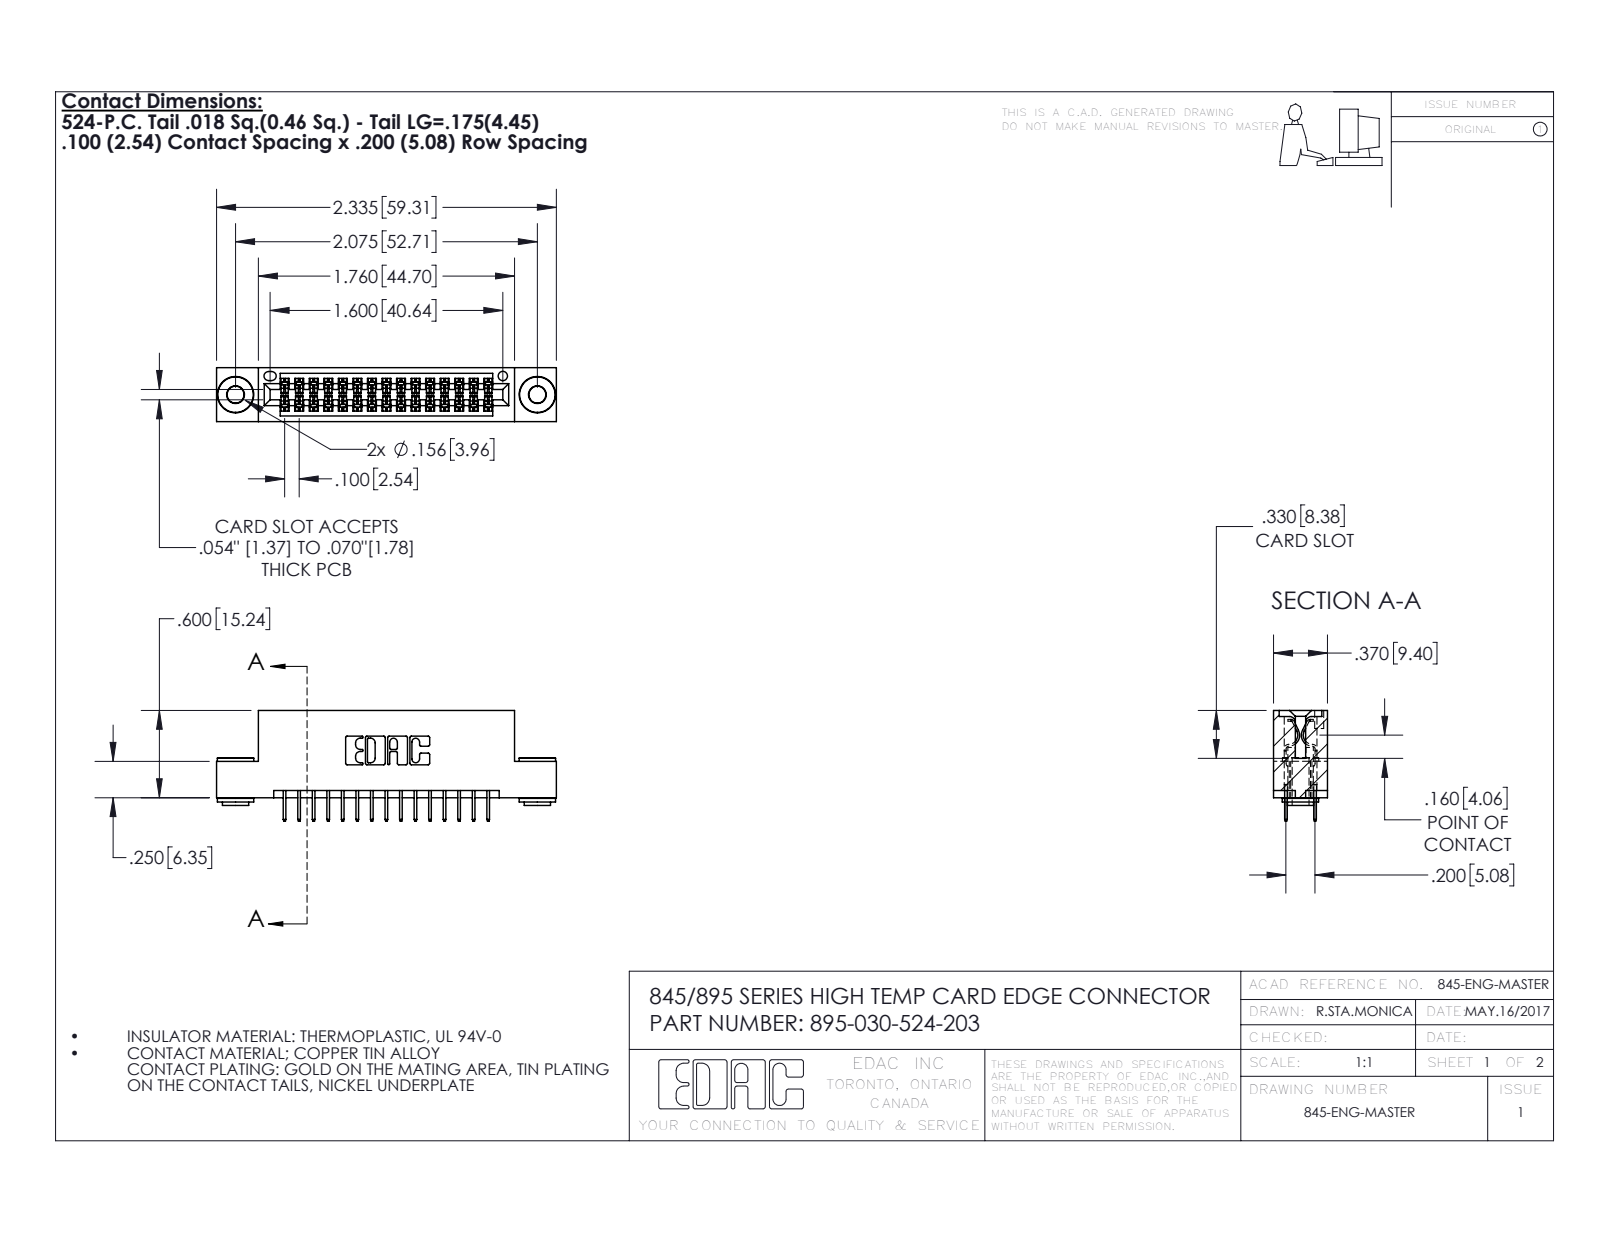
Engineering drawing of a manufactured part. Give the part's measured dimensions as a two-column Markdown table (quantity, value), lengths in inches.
| quantity | value |
| --- | --- |
| part name | 395-030-524-203; 345-292-001_345-293-124; 345 Part_Flush Mounting Lugs - 0.156 Dia-TH; 345-250-002_345-250-002-102 |
| STEP written by | SolidWorks 2016 (CONFIG_CONTROL_DESIGN) |
| units | inches |
| bodies | 33 solids, 1784 faces (1260 planar, 516 cylindrical, 8 other) |
| overall size | 2.335 × 0.762 × 0.37 |
| volume | 0.335 in³ |
| surface area | 11.89 in² |
| round holes (diameter × count) | 0.116 × 2, 0.156 × 2, 0.064 × 1 |
| round bosses / shafts (diameter × count) | 0.25 × 2, 0.18 × 2, 0.136 × 2 |
| partial cylindrical surfaces (radius × count) | 0.006 × 45, 0.01 × 22, 0.007 × 6, 0.031 × 6, 0.026 × 3, 0.014 × 2, 0.019 × 2, 0.022 × 2 |
| main face-to-face distances | 0.2, 0.072, 0.298, 0.37, 0.025, 0.098, 0.272, 0.225, 0.1, 0.072 |
| hole center spacings | 0.27, 1.842, 2.075 |
